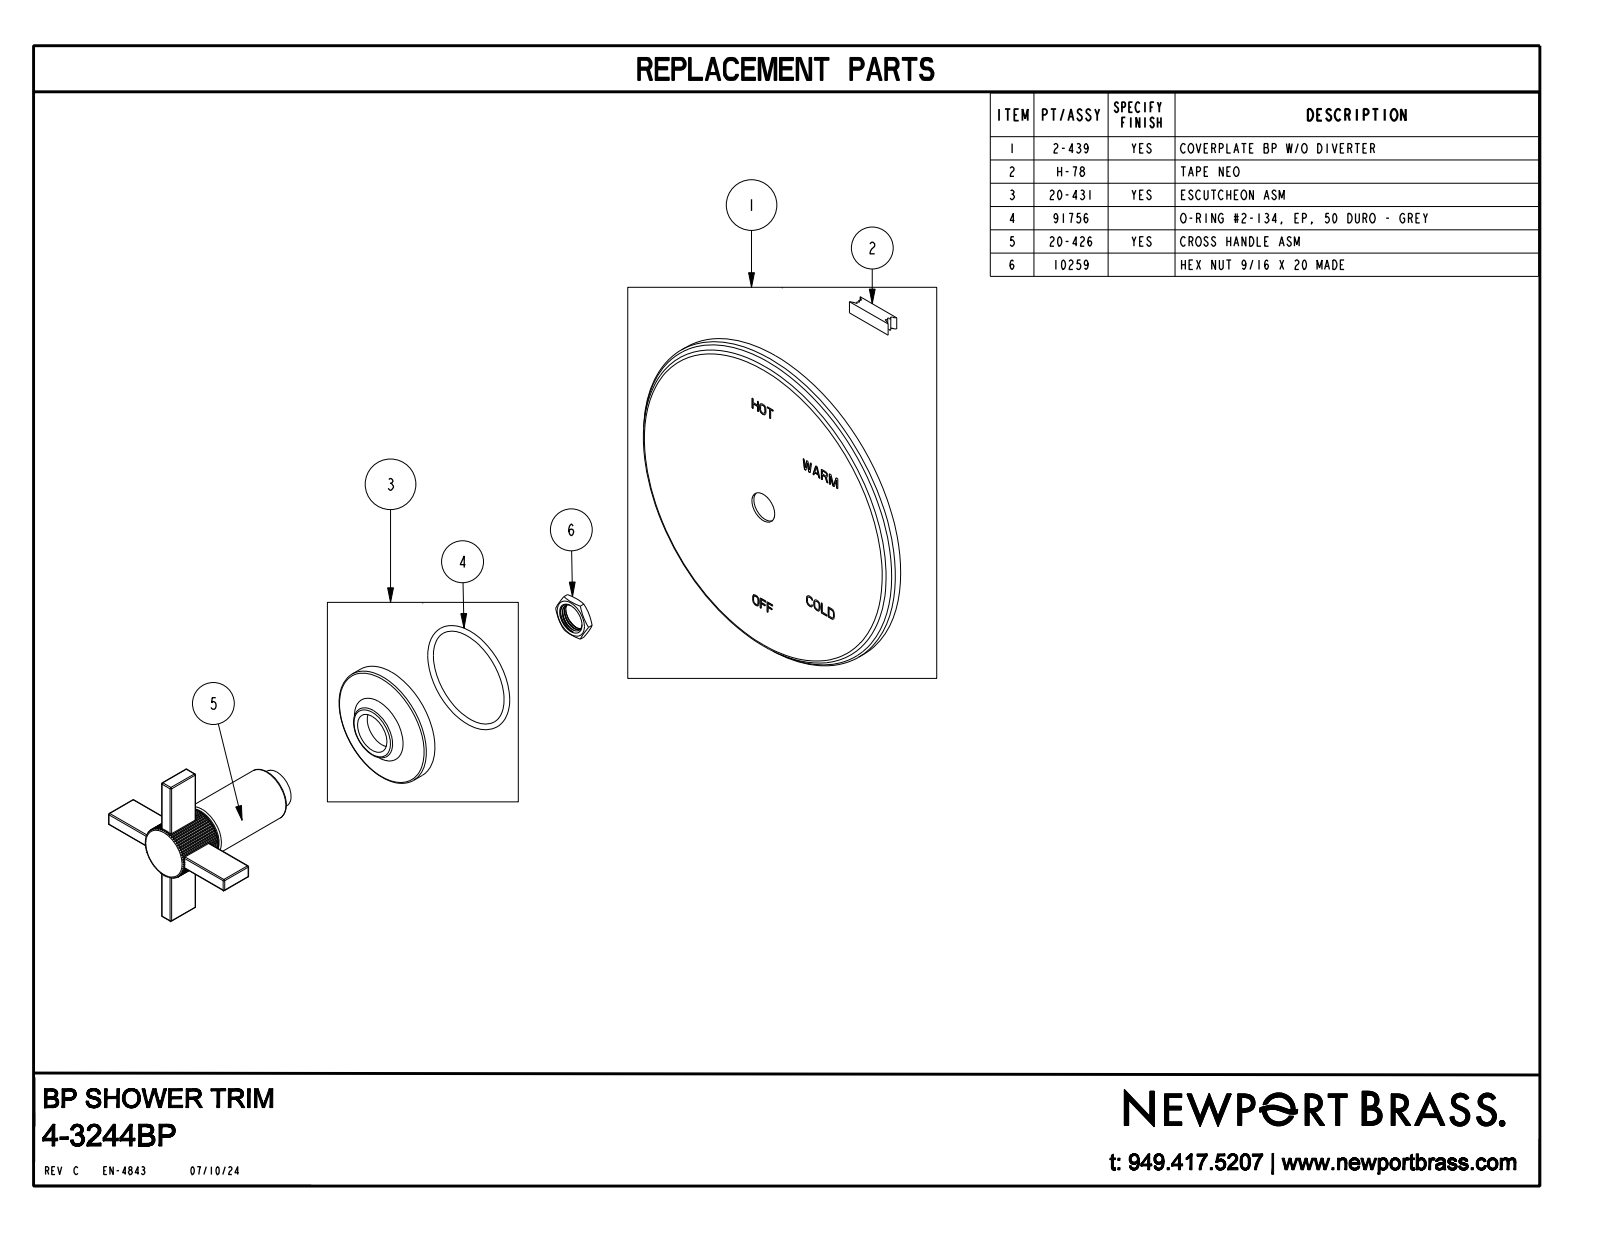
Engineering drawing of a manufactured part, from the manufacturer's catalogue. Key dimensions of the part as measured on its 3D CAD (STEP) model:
Part name (STEP PRODUCT): 11117; H-78; 2-439_ASM; 13118 (+8 more)
STEP written by: CREO PARAMETRIC BY PTC INC, 2018400 (CONFIG_CONTROL_DESIGN)
Units: inches
Bodies: 21 solids, 2573 faces (1126 planar, 931 cylindrical, 516 other)
Overall size (bounding box): 6.5 × 6.5 × 3.514
Volume: 5.16 in³ · Surface area: 194.7 in²
Round holes (diameter × count): ⌀0.11 ×5, ⌀0.15 ×4, ⌀0.14 ×1, ⌀0.275 ×1, ⌀0.335 ×1, ⌀0.358 ×1, ⌀0.375 ×1, ⌀0.383 ×1, ⌀0.397 ×1, ⌀0.4 ×1, ⌀0.42 ×1, ⌀0.516 ×1
Round bosses / shafts (diameter × count): ⌀0.138 ×5, ⌀6.5 ×1, ⌀2.25 ×1, ⌀1.812 ×1, ⌀1 ×1, ⌀0.85 ×1, ⌀0.73 ×1, ⌀0.572 ×1
Partial cylindrical surfaces — rounded edges, fillets, slot ends (radius × count): R0.02 ×40, R0.1 ×12, R0.03 ×8, R0.094 ×8, R0.01 ×6, R0.042 ×6, R0.072 ×1, R0.137 ×1
Main face-to-face distances: 0.05, 0.25, 0.225, 2.321, 0.3, 2.546, 3.196, 2.496, 3.146, 0.65
Hole centre spacings: 0.335, 0.474, 0.67
